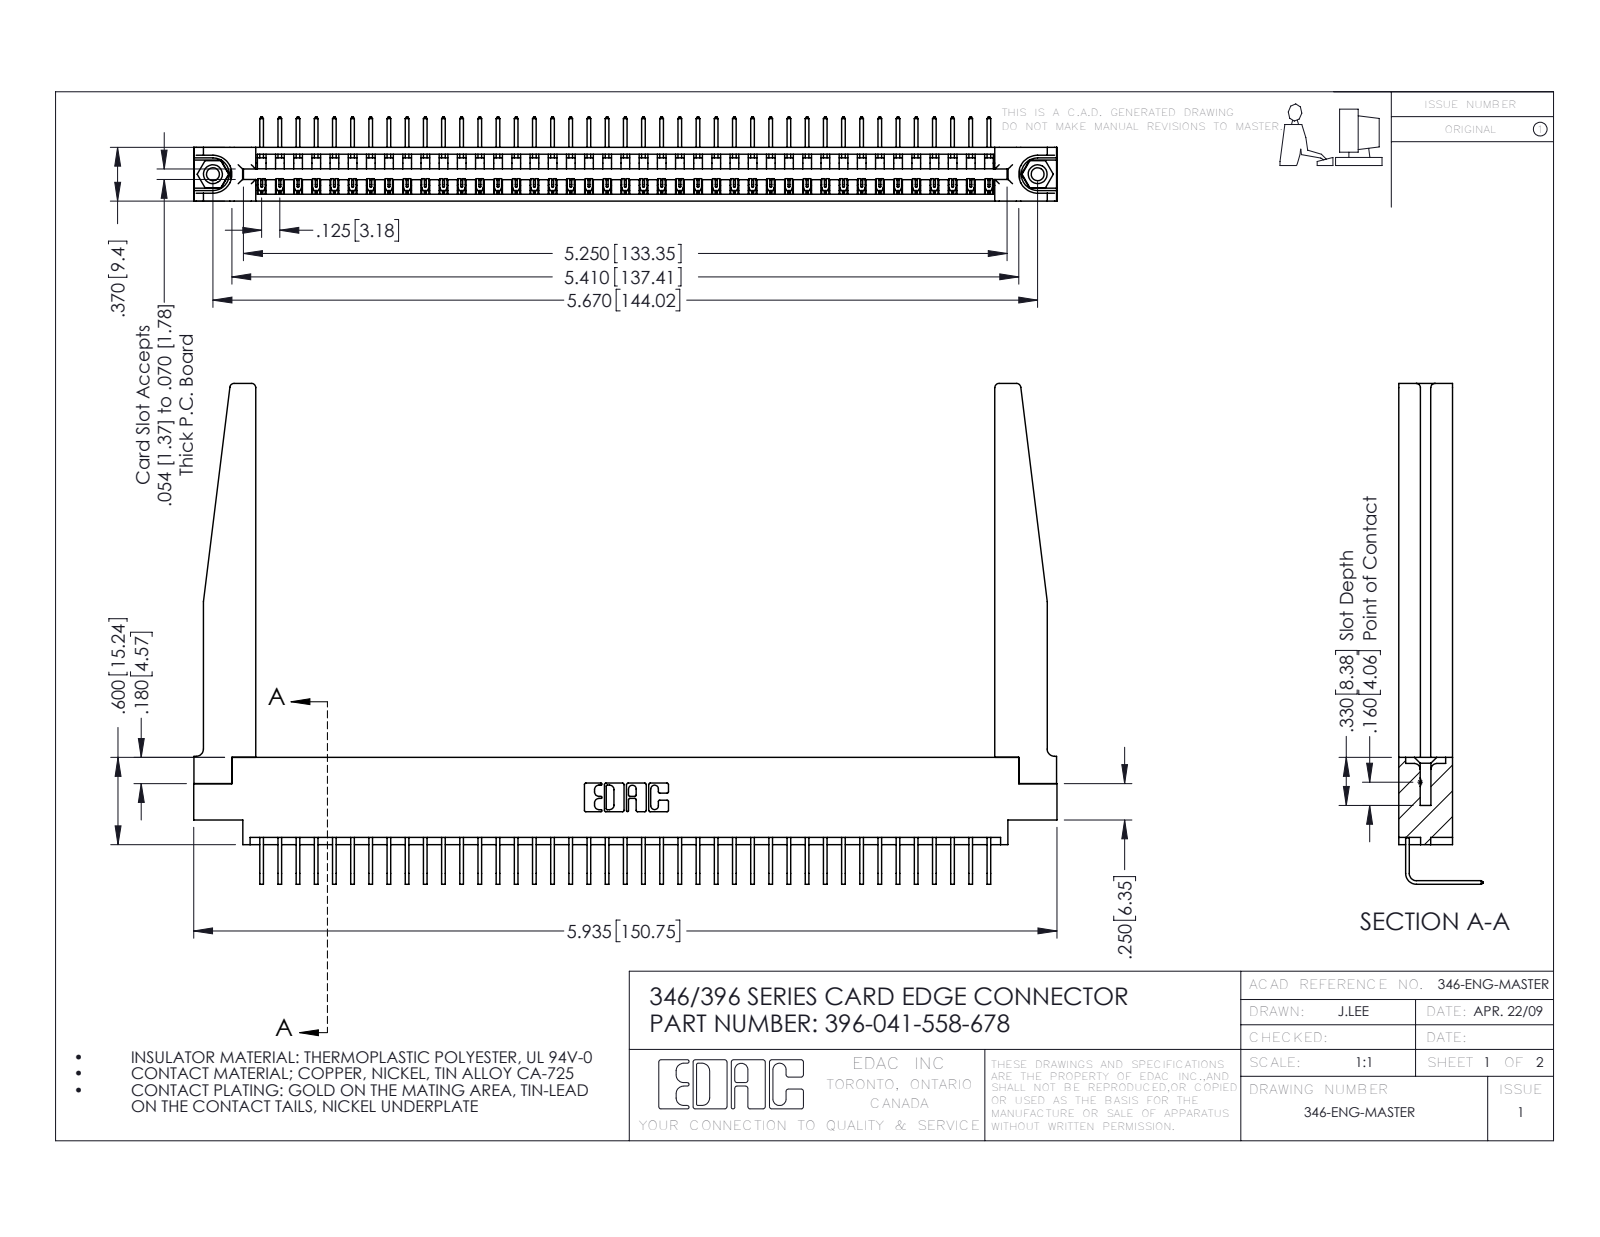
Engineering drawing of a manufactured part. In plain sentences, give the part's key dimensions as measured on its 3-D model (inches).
The part is named "346-220-078_345-220-078; 396-041-558-678; 345-292-001_558 Tail - 2; 346 Part_0.170 Offset - 0.156 Dia-TH (+1 more)". Its 3-D file was written by "SolidWorks 2016 (CONFIG_CONTROL_DESIGN)". It is 46 solids with 2820 faces: 1944 planar, 824 cylindrical and 52 other. Overall it measures 5.935 by 3.443 by 0.58 inches. Its volume is 1.301 cubic inches and its surface area 39.54 square inches. Round holes: 2 of diameter 0.089, 2 of diameter 0.125, 2 of diameter 0.156, 1 of diameter 0.064. Round bosses or shafts: 2 of diameter 0.155. Partial cylindrical surfaces (rounded edges, fillets, slot ends): 82 of radius 0.006, 22 of radius 0.01, 8 of radius 0.03, 6 of radius 0.007, 6 of radius 0.031, 3 of radius 0.026, 3 of radius 0.05, 2 of radius 0.031. The main face-to-face distances are 0.37, 0.322, 0.048, 0.072, 0.148, 0.15, 0.298, 0.025, 0.25, 0.222. The hole center spacings are 0.246, 5.461, 5.67.
